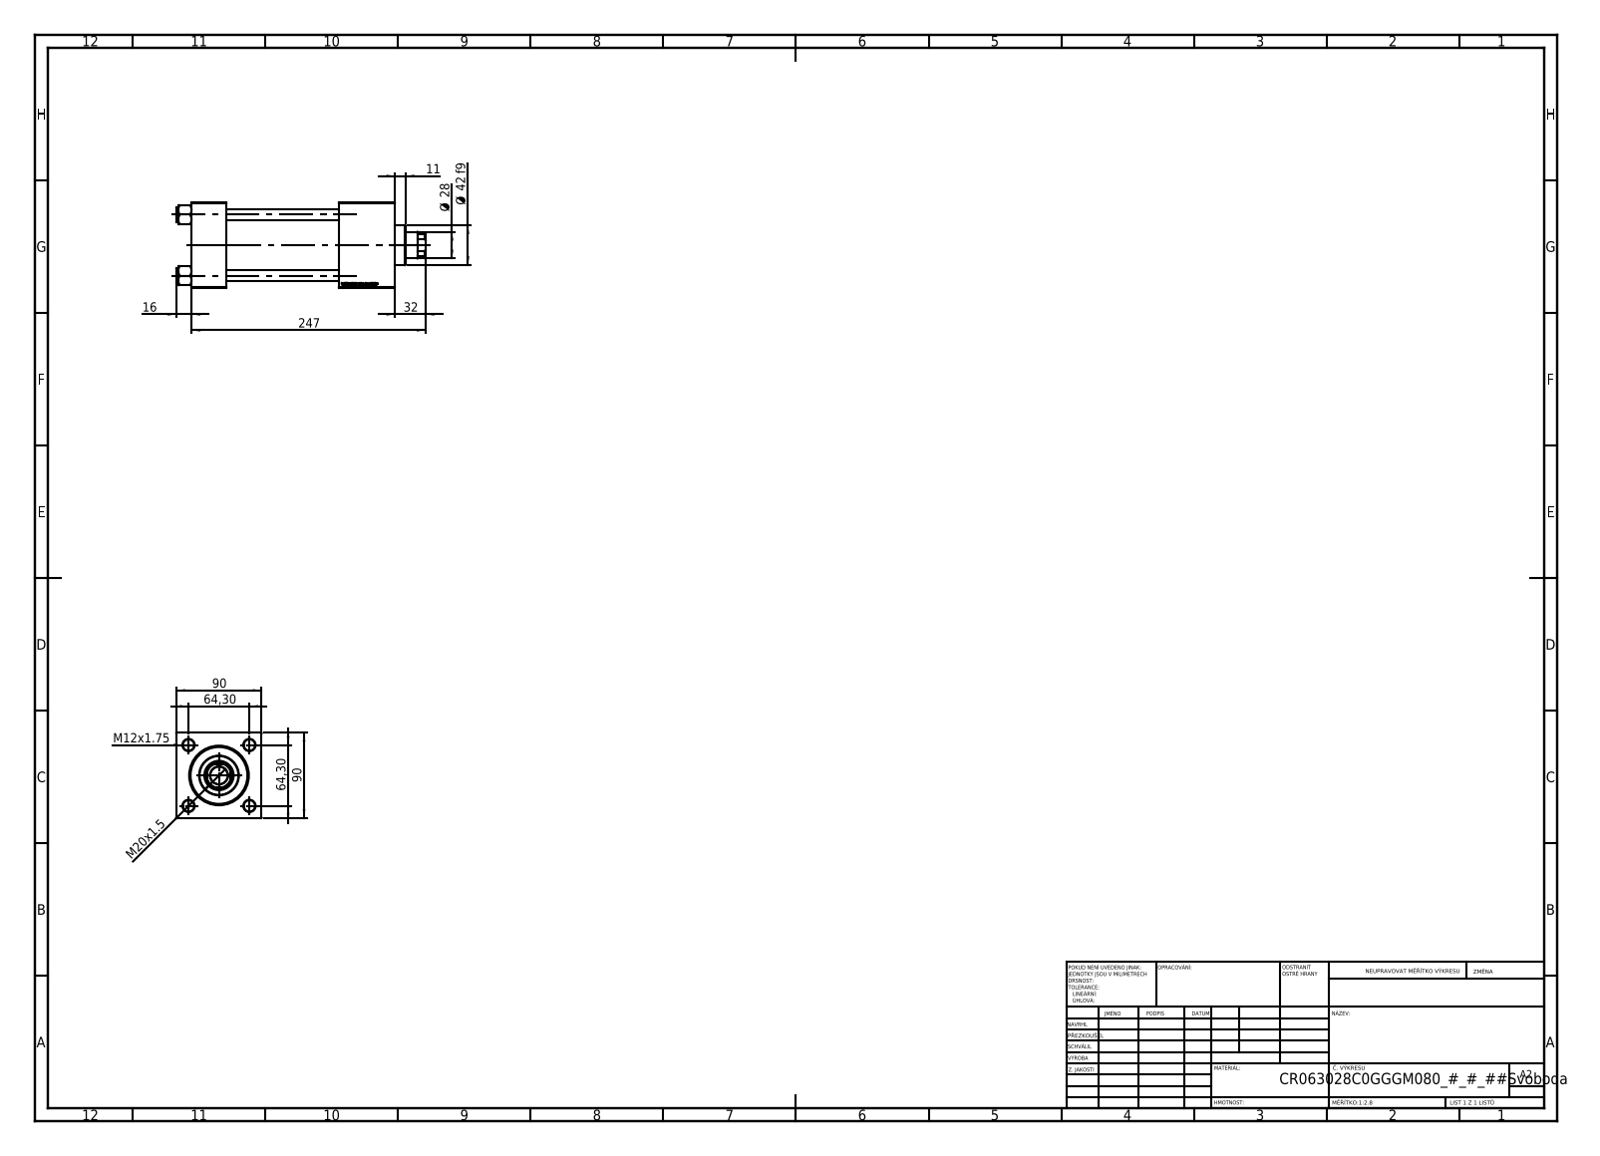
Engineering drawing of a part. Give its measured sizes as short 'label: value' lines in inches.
name: V215CR_VCP_C; NUT_M5_C; V215_VC_A; V215CR_C_TYCINKA (+1 more)
written by: SolidWorks 2019 (CONFIG_CONTROL_DESIGN)
unit: in
bodies: 11 solids, 1149 faces (526 planar, 87 cylindrical, 536 other)
size: 10.354 × 3.543 × 3.543
volume: 63.95 in³; area: 338.4 in²
holes: 4× ⌀0.472, 2× ⌀0.276, 2× ⌀0.825, 2× ⌀1.181, 1× ⌀0.728, 1× ⌀1.102, 1× ⌀1.22, 1× ⌀1.969, 1× ⌀2.362, 1× ⌀2.48
bosses: 4× ⌀0.591, 1× ⌀2.717, 1× ⌀1.654
rounds: 1× R0.531
face distances: 3.543, 1.457, 8.465, 7.008, 6.142, 4.685, 2.323, 7.335, 5.878, 1.193
hole spacings: 1.79, 2.531, 3.58, 6.201
